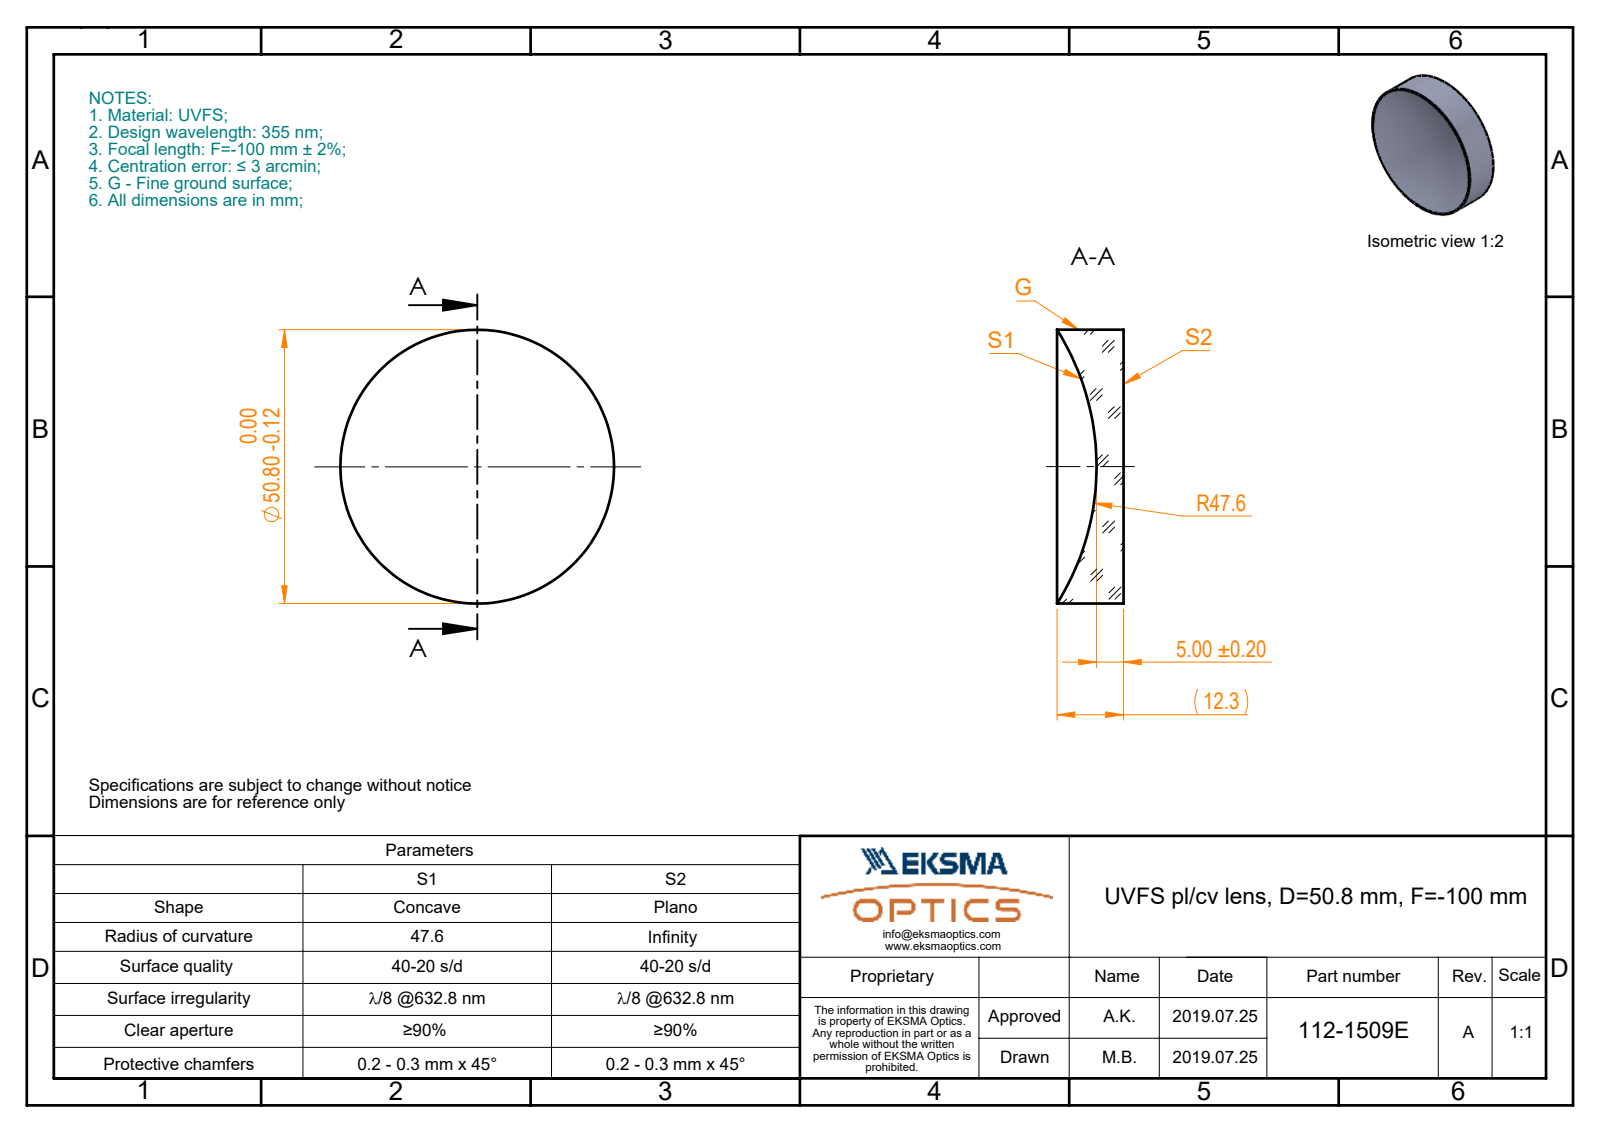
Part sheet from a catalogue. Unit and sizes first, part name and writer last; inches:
Units: inches
Overall size (bounding box): 2 × 2 × 0.486
Round bosses / shafts (diameter × count): ⌀2 ×1
Volume: 1.06 in³ · Surface area: 9.599 in²
Bodies: 1 solid, 5 faces (1 planar, 2 cylindrical, 2 other)
Part name (STEP PRODUCT): 112-1509E UVFS pl-cv 50.8 F-100
STEP written by: SolidWorks 2017 (CONFIG_CONTROL_DESIGN)
